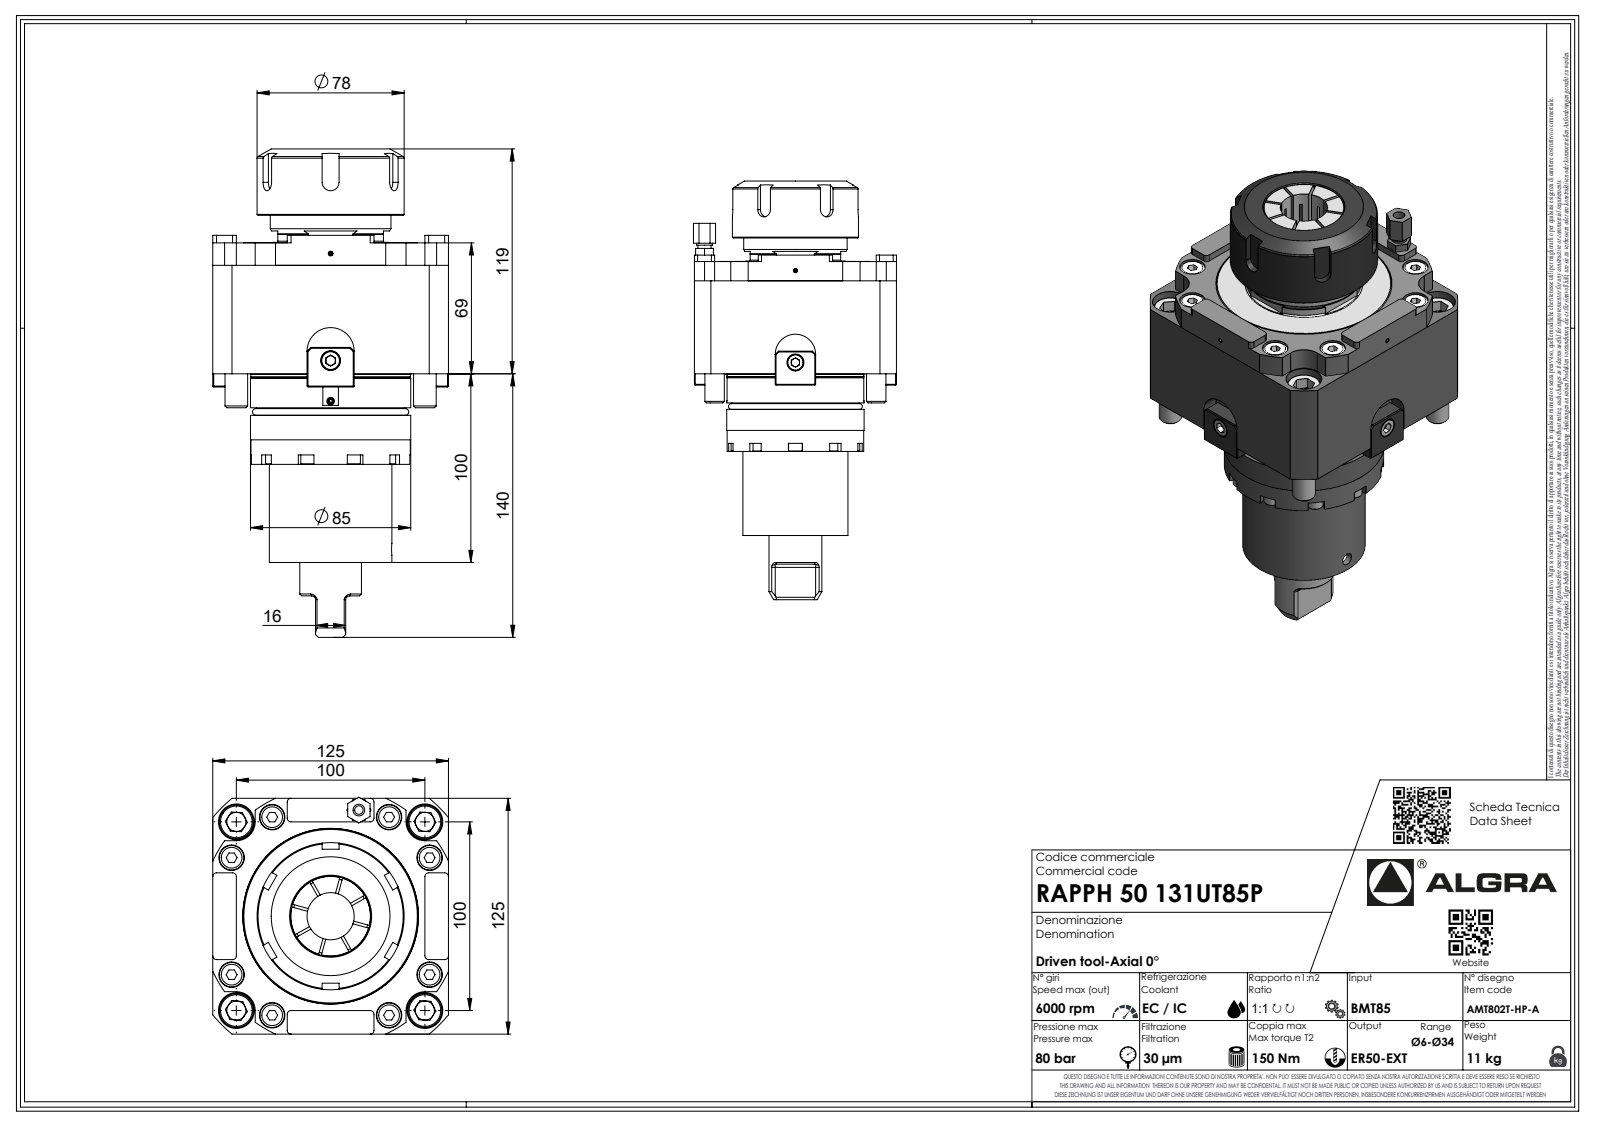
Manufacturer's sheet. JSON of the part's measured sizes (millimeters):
{"part_name": "RAPPH50131UT85P", "step_written_by": "SolidWorks 2023 (AUTOMOTIVE_DESIGN)", "units": "millimeters", "bodies": {"solids": 1, "faces": 653, "planar": 428, "cylindrical": 100, "other": 125}, "overall_size": [258.9, 125, 125], "volume_mm3": 1728000, "surface_area_mm2": 114609, "round_holes": [[4.5, 2], [2.1, 1]], "round_bosses_or_shafts": [[12, 3], [85, 1], [84.6, 1], [84.5, 1], [78, 1], [65, 1], [64, 1], [32.7, 1]], "partial_cylinders_radius": [[2, 22], [4.35, 10], [0.33, 7], [0.52, 7], [3.7, 7], [10, 4], [4.5, 3], [12.5, 2]], "face_to_face_distances": [125, 69.4, 69.5, 119.2, 49.8, 49.7, 100, 12, 169.4, 169.5]}
